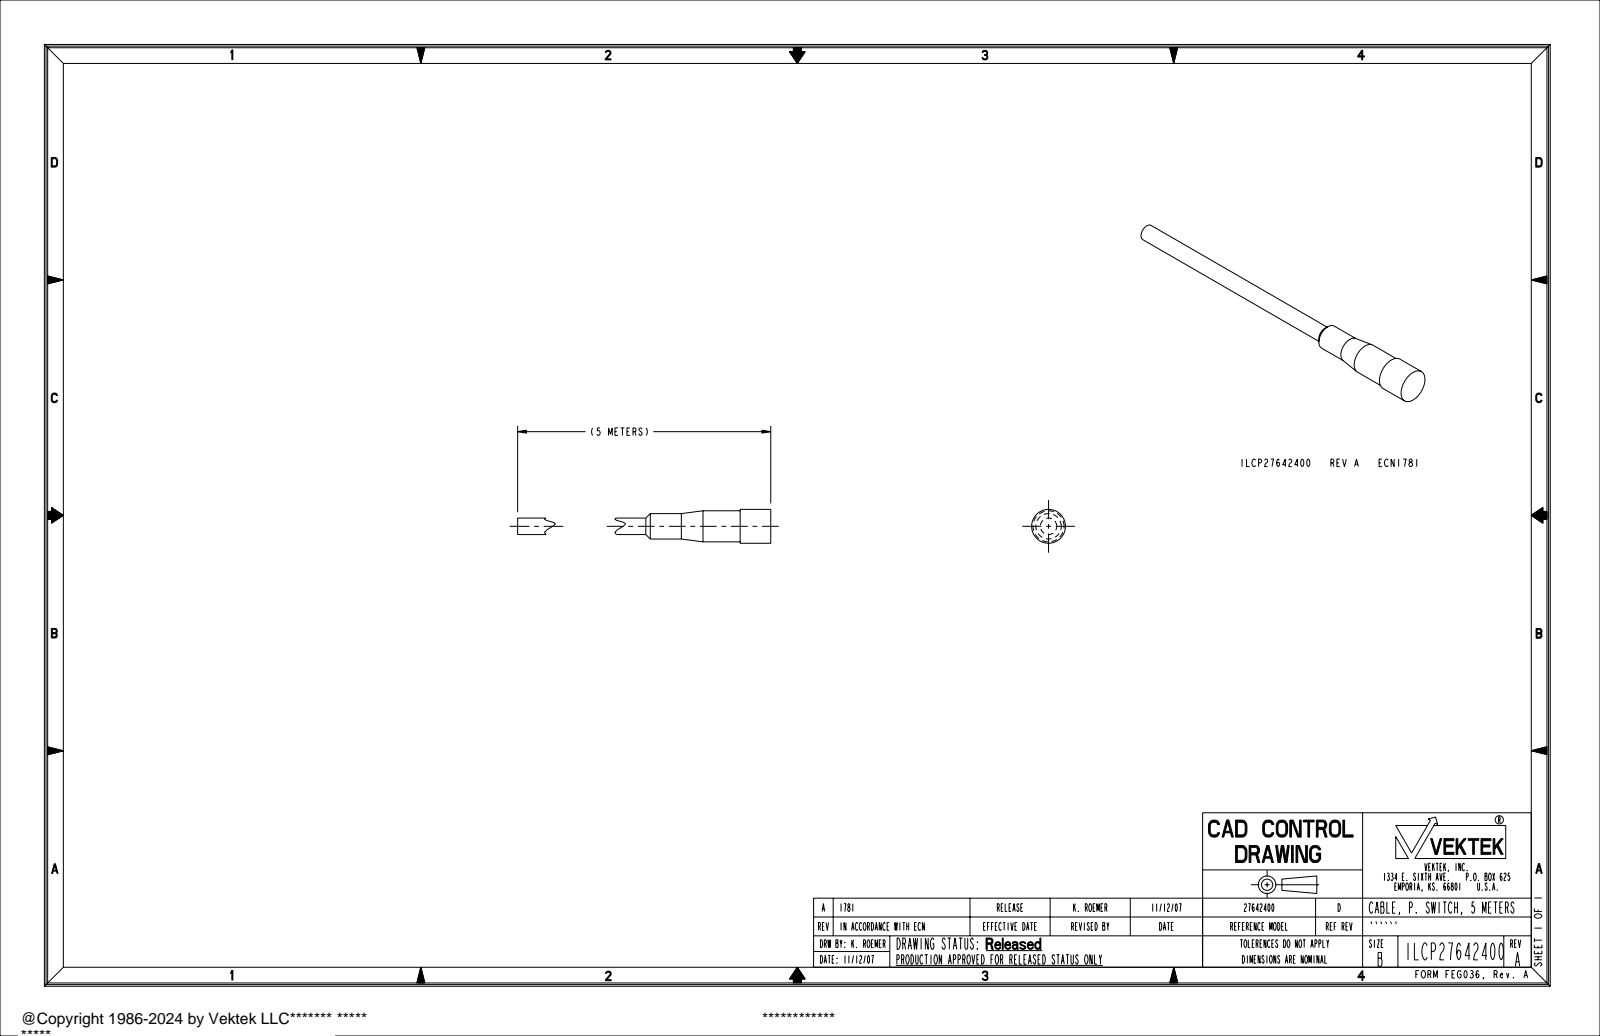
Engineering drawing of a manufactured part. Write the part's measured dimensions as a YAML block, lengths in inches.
part_name: "ILCP27642400"
step_written_by: "PRO/ENGINEER BY PARAMETRIC TECHNOLOGY CORPORATION, 2005180 (AUTOMOTIVE_DESIGN_CC2)"
units: inches
bodies: {solids: 1, faces: 15, planar: 3, cylindrical: 8, other: 4}
overall_size: [4, 0.36, 0.36]
volume: 0.168
surface_area: 2.934
round_bosses_or_shafts:
  - {diameter: 0.36, count: 1}
  - {diameter: 0.33, count: 1}
  - {diameter: 0.27, count: 1}
  - {diameter: 0.175, count: 1}
face_to_face_distances: [4, 3.675, 0.325]
